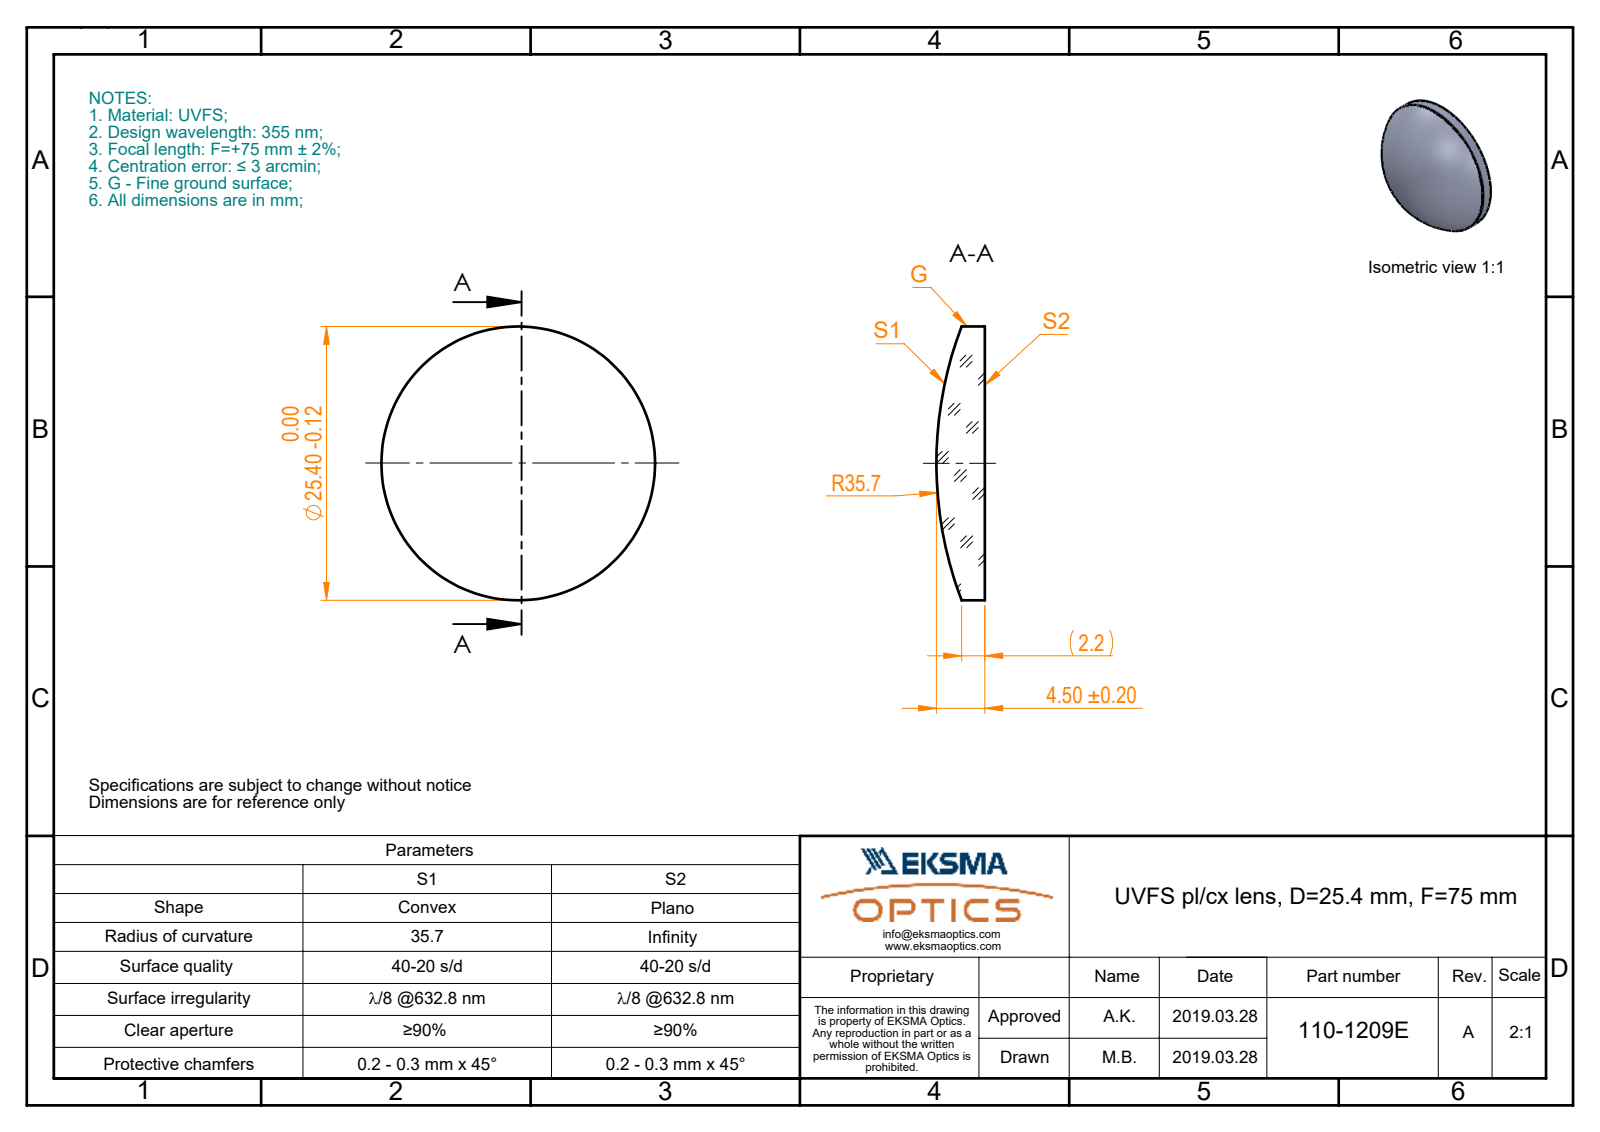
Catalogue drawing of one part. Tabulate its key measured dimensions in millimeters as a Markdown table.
| quantity | value |
| --- | --- |
| part name | 110-1209E UVFS pl-cx 25.4 F75 |
| STEP written by | SolidWorks 2017 (CONFIG_CONTROL_DESIGN) |
| units | millimeters |
| bodies | 1 solid, 5 faces (1 planar, 2 cylindrical, 2 other) |
| overall size | 25.4 × 25.4 × 4.5 |
| volume | 1 695 mm³ |
| surface area | 1 203 mm² |
| round bosses / shafts (diameter × count) | 25.4 × 1 |
